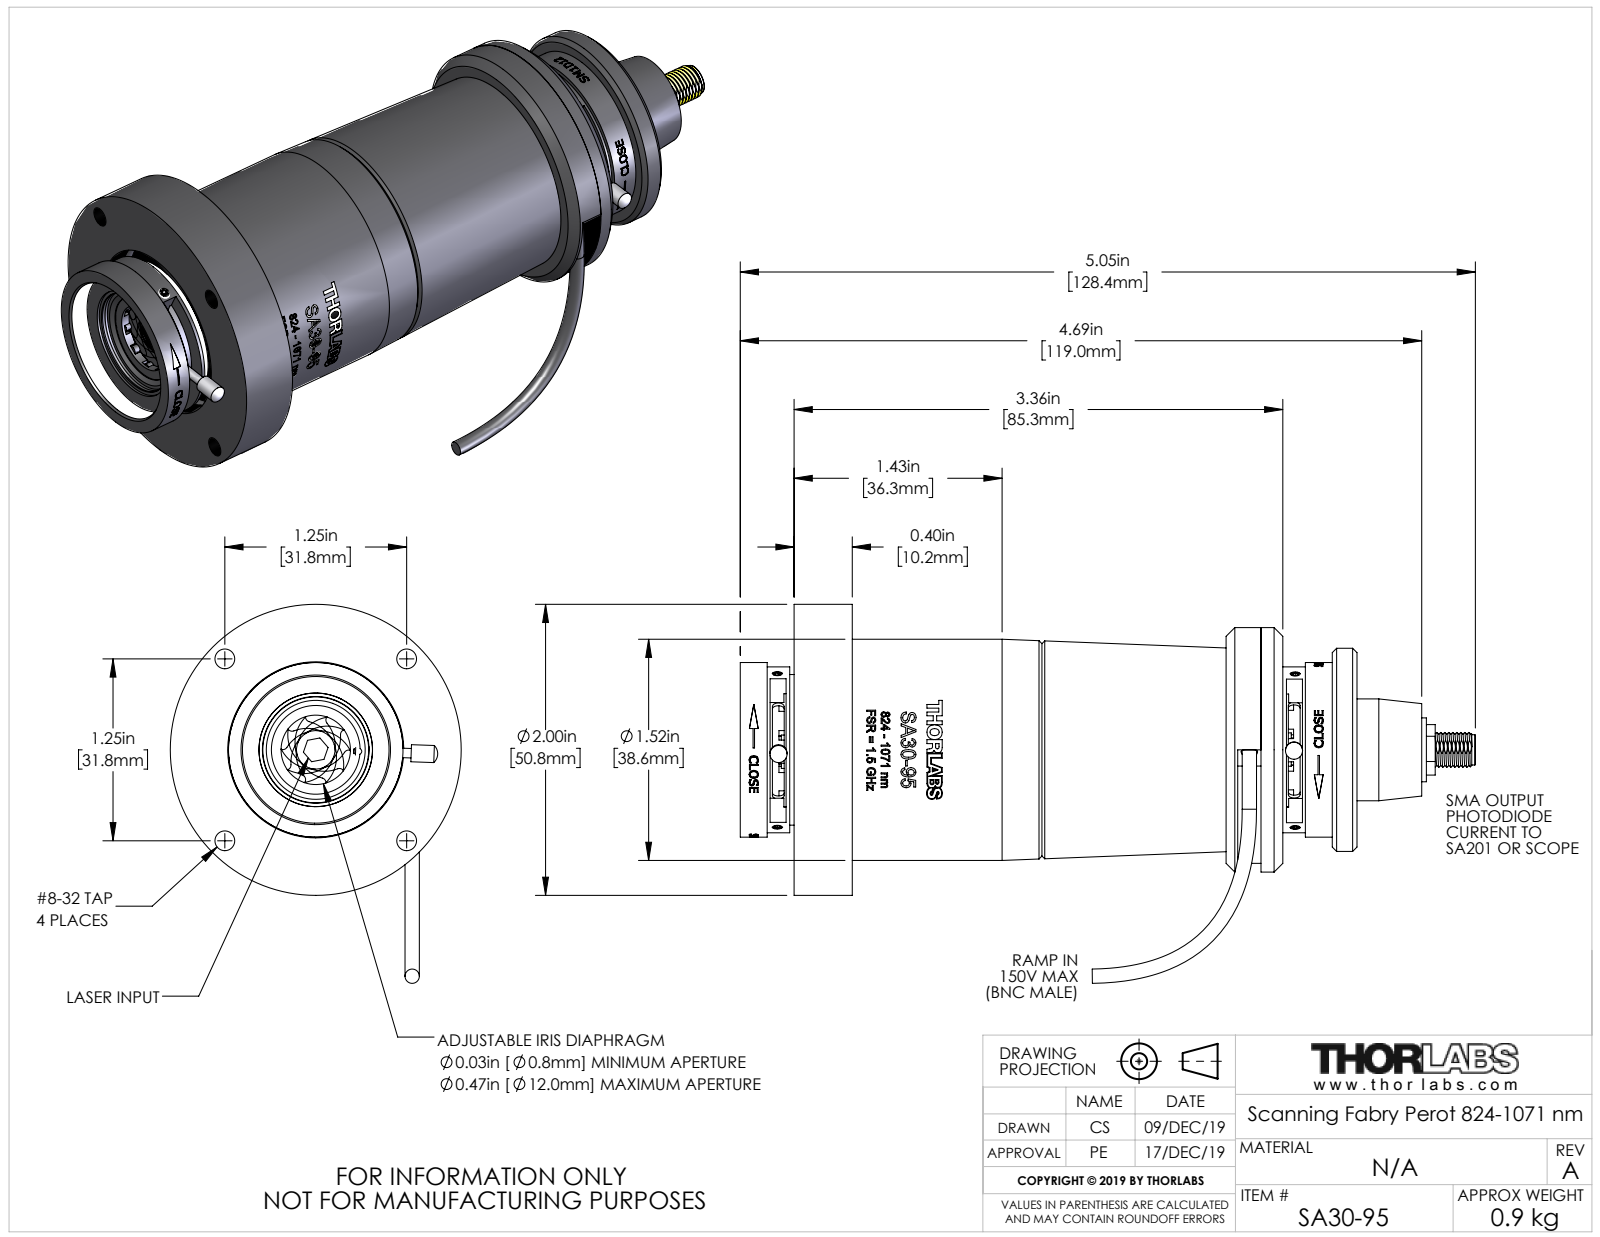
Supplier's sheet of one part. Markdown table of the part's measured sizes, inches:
| quantity | value |
| --- | --- |
| part name | STN052139-E0W |
| STEP written by | SolidWorks 2018 (AUTOMOTIVE_DESIGN) |
| units | inches |
| bodies | 42 solids, 1577 faces (619 planar, 532 cylindrical, 426 other) |
| overall size | 5.054 × 2.605 × 2 |
| volume | 3.331 in³ |
| surface area | 71.3 in² |
| round holes (diameter × count) | 0.066 × 20, 0.136 × 4, 0.043 × 2, 0.063 × 2, 0.039 × 1, 0.113 × 1, 0.181 × 1, 0.25 × 1, 0.325 × 1, 0.385 × 1, 0.4 × 1, 0.474 × 1 |
| round bosses / shafts (diameter × count) | 0.06 × 20, 0.065 × 15, 0.065 × 7, 0.086 × 4, 0.117 × 2, 0.064 × 2, 2 × 1, 1.68 × 1 |
| partial cylindrical surfaces (radius × count) | 0.033 × 20, 0.033 × 20, 0.063 × 20, 0.251 × 20, 0.378 × 20, 0.024 × 2, 0.13 × 2, 1 × 2 |
| main face-to-face distances | 3.21, 0.15, 3.418, 0.51, 3.375, 0.045, 3.373, 0.043, 0.4, 2.81 |
| hole center spacings | 0.343, 0.472, 0.292, 0.556, 0.584, 0.172, 0.18, 0.181 |
